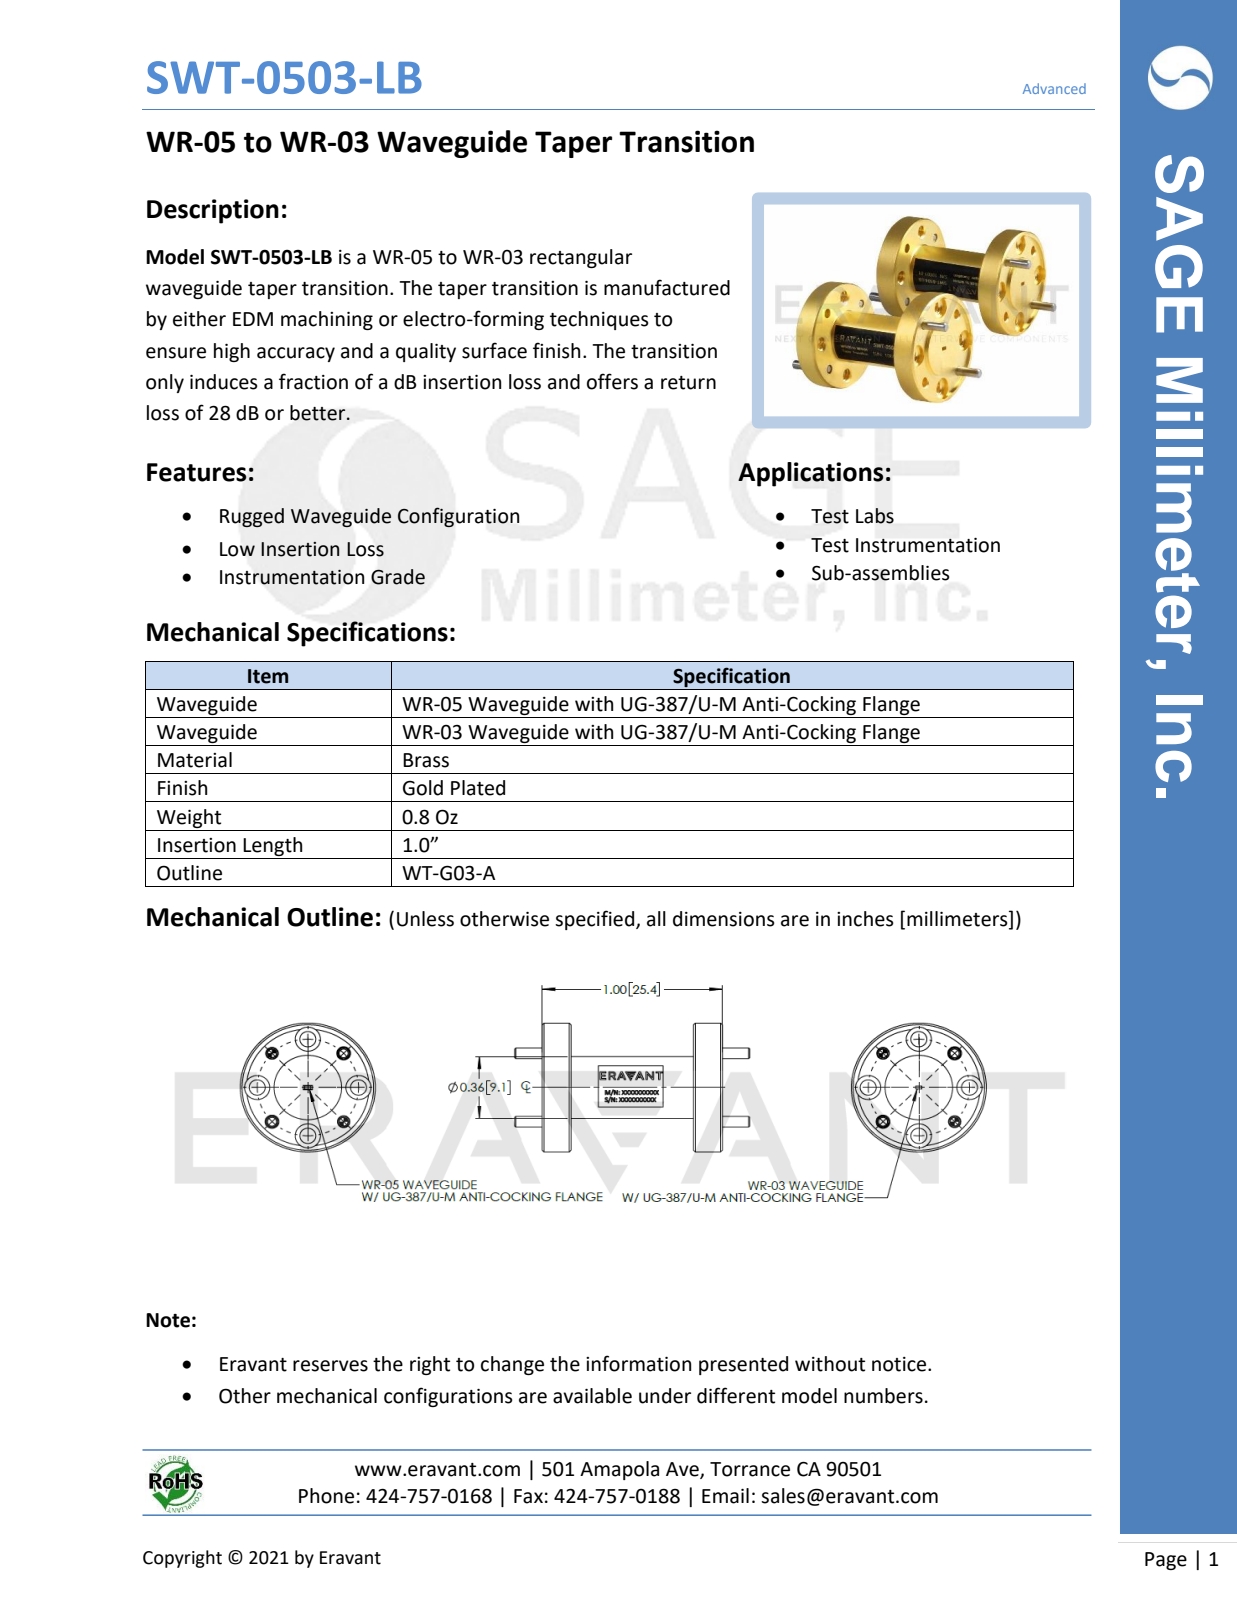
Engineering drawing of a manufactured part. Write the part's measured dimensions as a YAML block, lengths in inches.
part_name: "WT-G03-A"
step_written_by: "SolidWorks 2021 (CONFIG_CONTROL_DESIGN)"
units: inches
bodies: {solids: 5, faces: 148, planar: 34, cylindrical: 74, other: 40}
overall_size: [1.305, 0.75, 0.75]
volume: 0.19
surface_area: 3.865
round_holes:
  - {diameter: 0.061, count: 4}
  - {diameter: 0.067, count: 4}
  - {diameter: 0.089, count: 4}
  - {diameter: 0.14, count: 4}
  - {diameter: 0.68, count: 1}
round_bosses_or_shafts:
  - {diameter: 0.063, count: 4}
  - {diameter: 0.75, count: 1}
  - {diameter: 0.375, count: 1}
  - {diameter: 0.36, count: 1}
face_to_face_distances: [0.98, 0.02, 0.68, 0.82, 0.14, 0.14, 0.82, 0.96, 0.16, 0.84]
hole_center_spacings: [0.215, 0.52, 0.398, 0.281, 0.281, 0.563, 0.398, 0.216]
